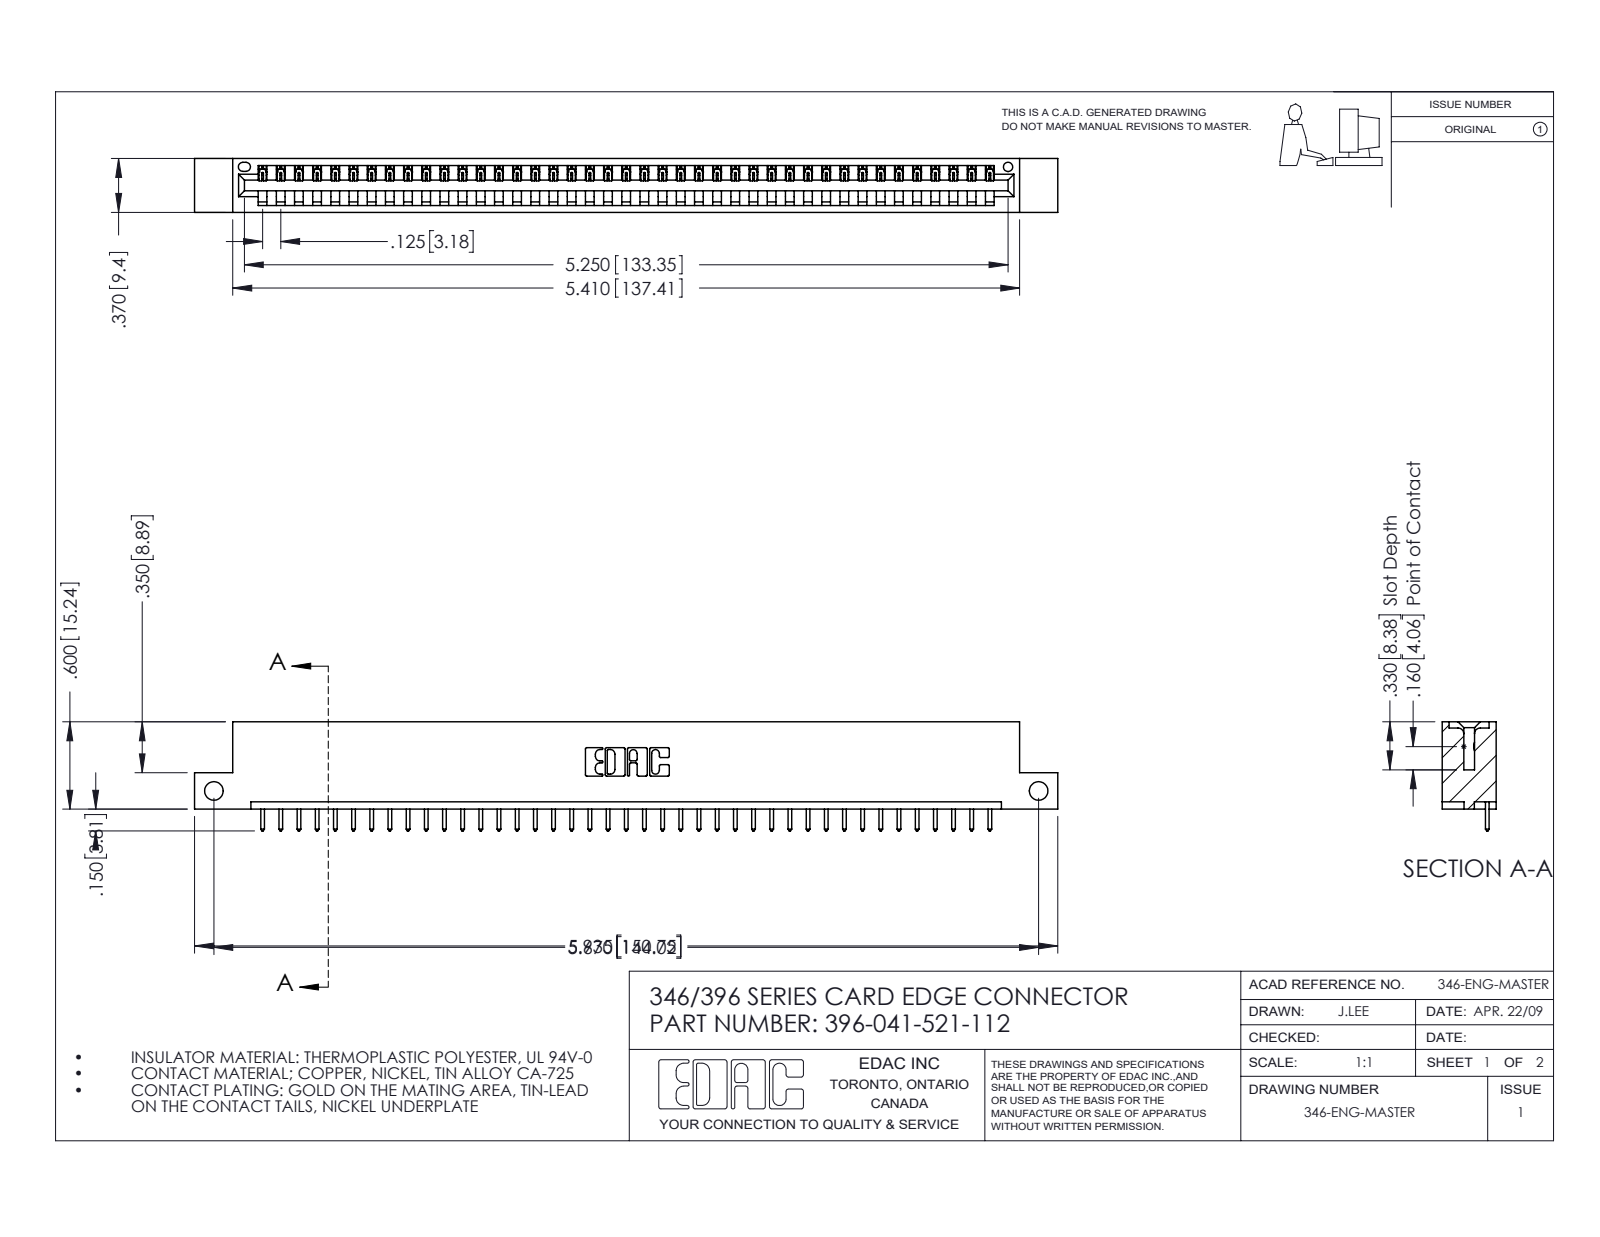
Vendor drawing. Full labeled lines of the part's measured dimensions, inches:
Part name (STEP PRODUCT): 346 Part_Flush Mounting Lugs - Side Mount; 345-292-001_345-293-121; 396-041-521-112
STEP written by: SolidWorks 2016 (CONFIG_CONTROL_DESIGN)
Units: inches
Bodies: 42 solids, 2500 faces (1716 planar, 784 cylindrical, 0 other)
Overall size (bounding box): 5.935 × 0.75 × 0.37
Volume: 0.868 in³ · Surface area: 26.59 in²
Round holes (diameter × count): ⌀0.128 ×2, ⌀0.064 ×1
Partial cylindrical surfaces — rounded edges, fillets, slot ends (radius × count): R0.006 ×82, R0.01 ×82, R0.01 ×22, R0.007 ×6, R0.031 ×6, R0.026 ×3, R0.031 ×2, R0.04 ×2
Main face-to-face distances: 0.048, 0.322, 0.37, 0.25, 0.072, 0.298, 0.025, 0.148, 0.222, 0.1
Hole centre spacings: 5.67
